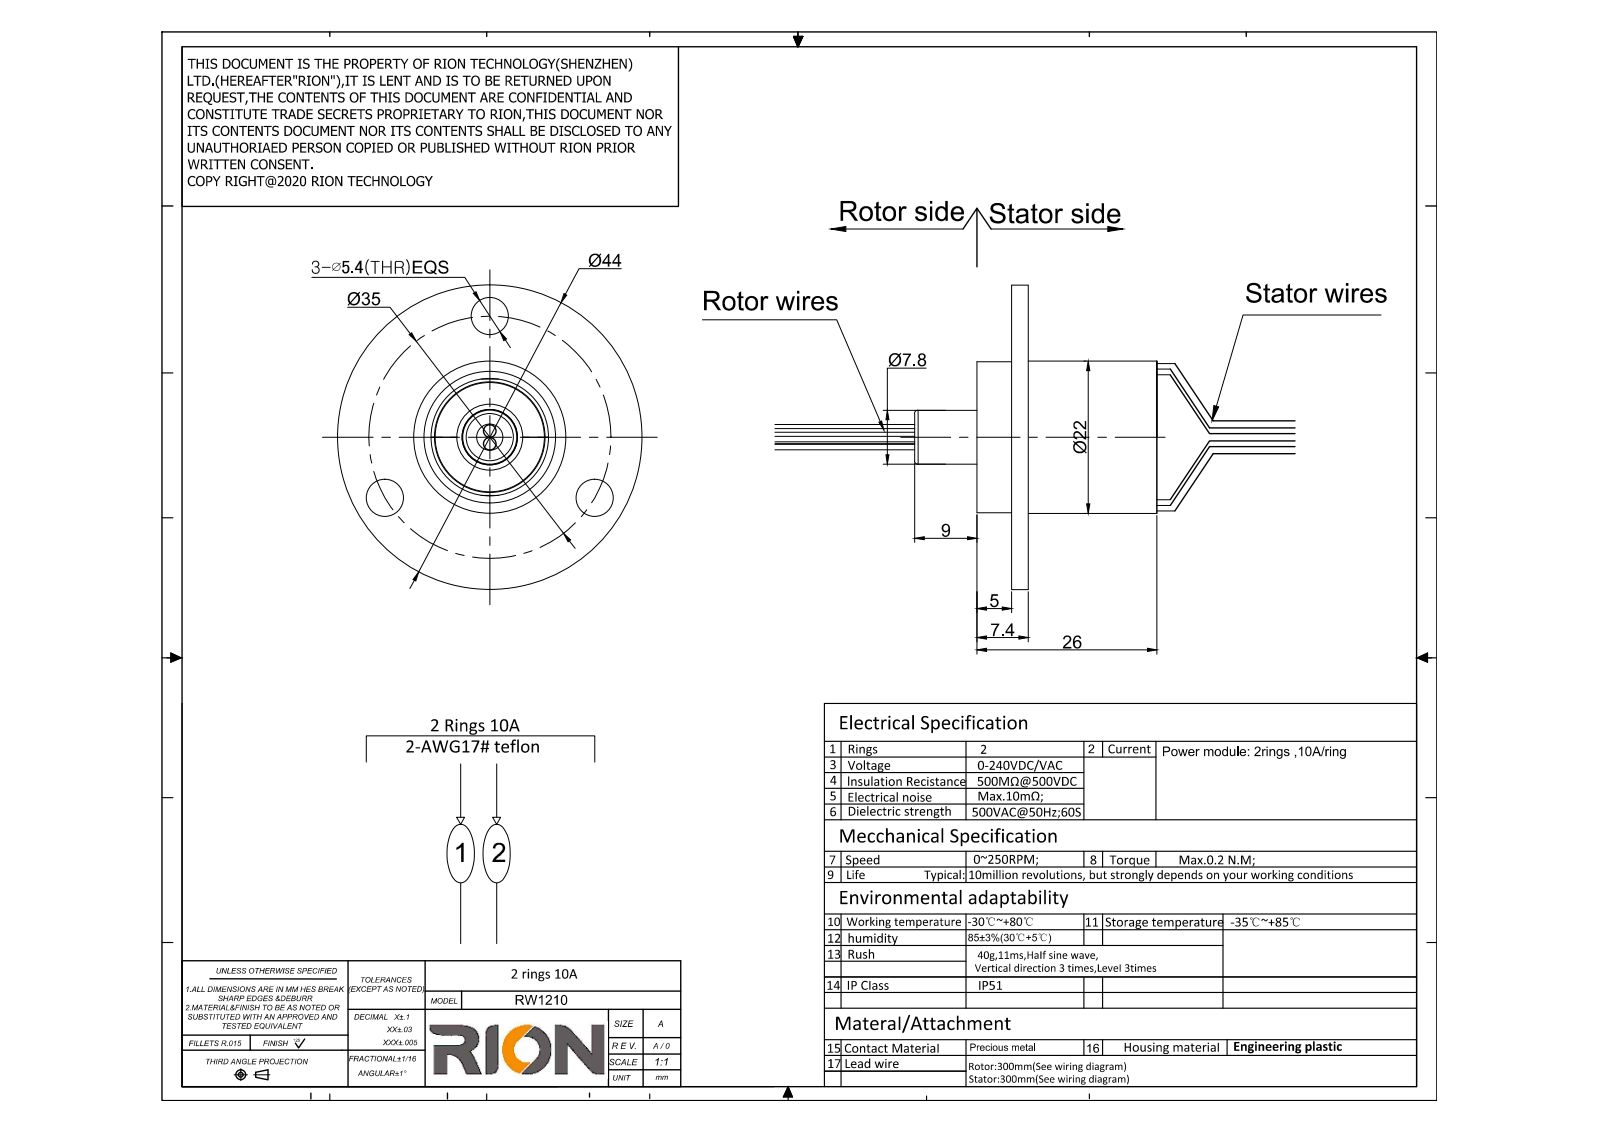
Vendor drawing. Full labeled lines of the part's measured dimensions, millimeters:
Part name (STEP PRODUCT): RW1210
STEP written by: SolidWorks 2014 (CONFIG_CONTROL_DESIGN)
Units: millimetres
Bodies: 1 solid, 55 faces (20 planar, 33 cylindrical, 2 other)
Overall size (bounding box): 63.9 × 44 × 44
Volume: 12 977 mm³ · Surface area: 5 768 mm²
Round holes (diameter × count): ⌀5.4 ×3, ⌀4 ×1, ⌀7 ×1, ⌀20 ×1
Round bosses / shafts (diameter × count): ⌀1.8 ×4, ⌀44 ×1, ⌀22 ×1, ⌀21.8 ×1, ⌀19.9 ×1, ⌀7.8 ×1, ⌀6.8 ×1
Main face-to-face distances: 2.4, 21, 18.6, 5, 7.4, 26, 9, 35, 14, 16.4
Hole centre spacings: 17.5, 30.31, 30.32
